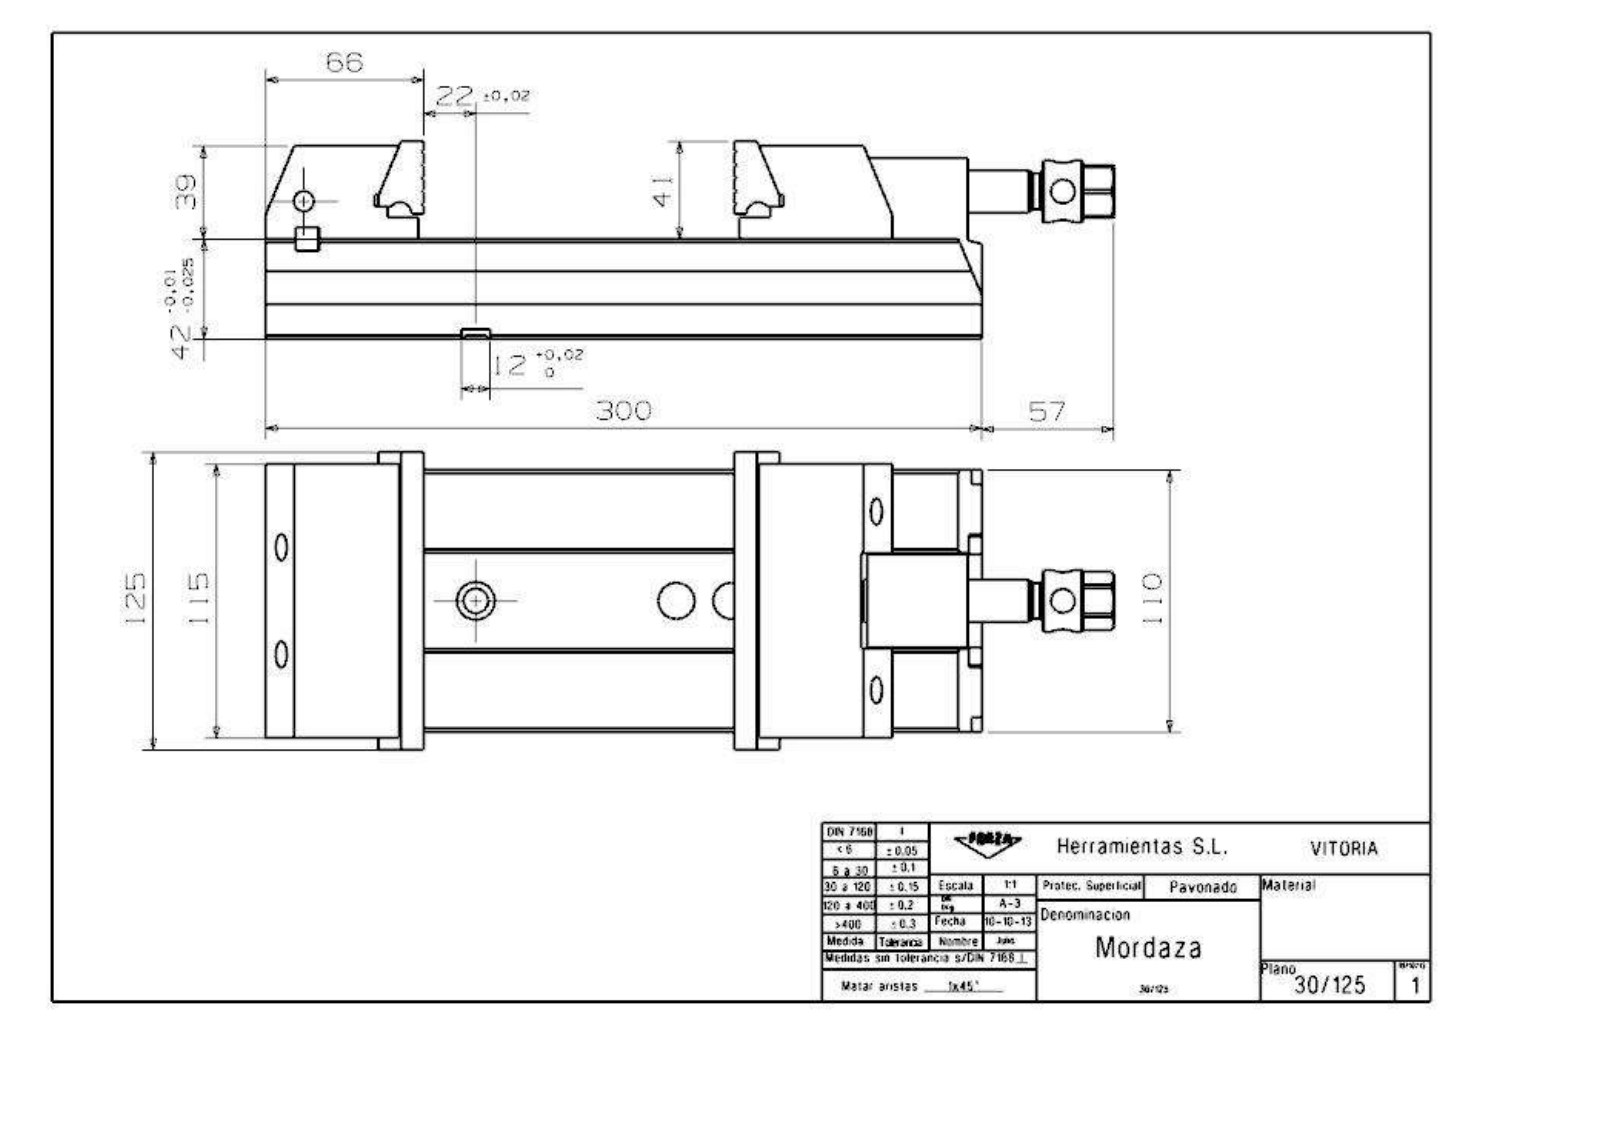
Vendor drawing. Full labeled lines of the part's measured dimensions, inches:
Part name (STEP PRODUCT): 30_125_Mordaza
STEP written by: SIEMENS PLM Software NX 7.5 (AUTOMOTIVE_DESIGN)
Units: inches
Bodies: 12 solids, 512 faces (320 planar, 147 cylindrical, 45 other)
Overall size (bounding box): 13.989 × 4.921 × 3.268
Volume: 99.04 in³ · Surface area: 445.6 in²
Round holes (diameter × count): ⌀0.171 ×5, ⌀0.204 ×4, ⌀0.256 ×4, ⌀0.295 ×4, ⌀0.453 ×4, ⌀0.346 ×3, ⌀0.275 ×2, ⌀0.315 ×2, ⌀0.394 ×2, ⌀0.413 ×2, ⌀0.433 ×2, ⌀0.487 ×2
Round bosses / shafts (diameter × count): ⌀1.024 ×1, ⌀0.698 ×1, ⌀0.591 ×1, ⌀0.571 ×1, ⌀0.413 ×1
Partial cylindrical surfaces — rounded edges, fillets, slot ends (radius × count): R0.012 ×20, R0.236 ×7, R0.394 ×4, R0.63 ×4, R0.063 ×2, R0.197 ×2, R0.118 ×1, R0.315 ×1
Main face-to-face distances: 1.654, 0.335, 0.606, 1.047, 3.031, 1.063, 1.535, 1.161, 0.098, 3.268
Hole centre spacings: 2.362, 0.362, 0.591, 0.918, 0.935, 1.002, 1.496, 1.732
